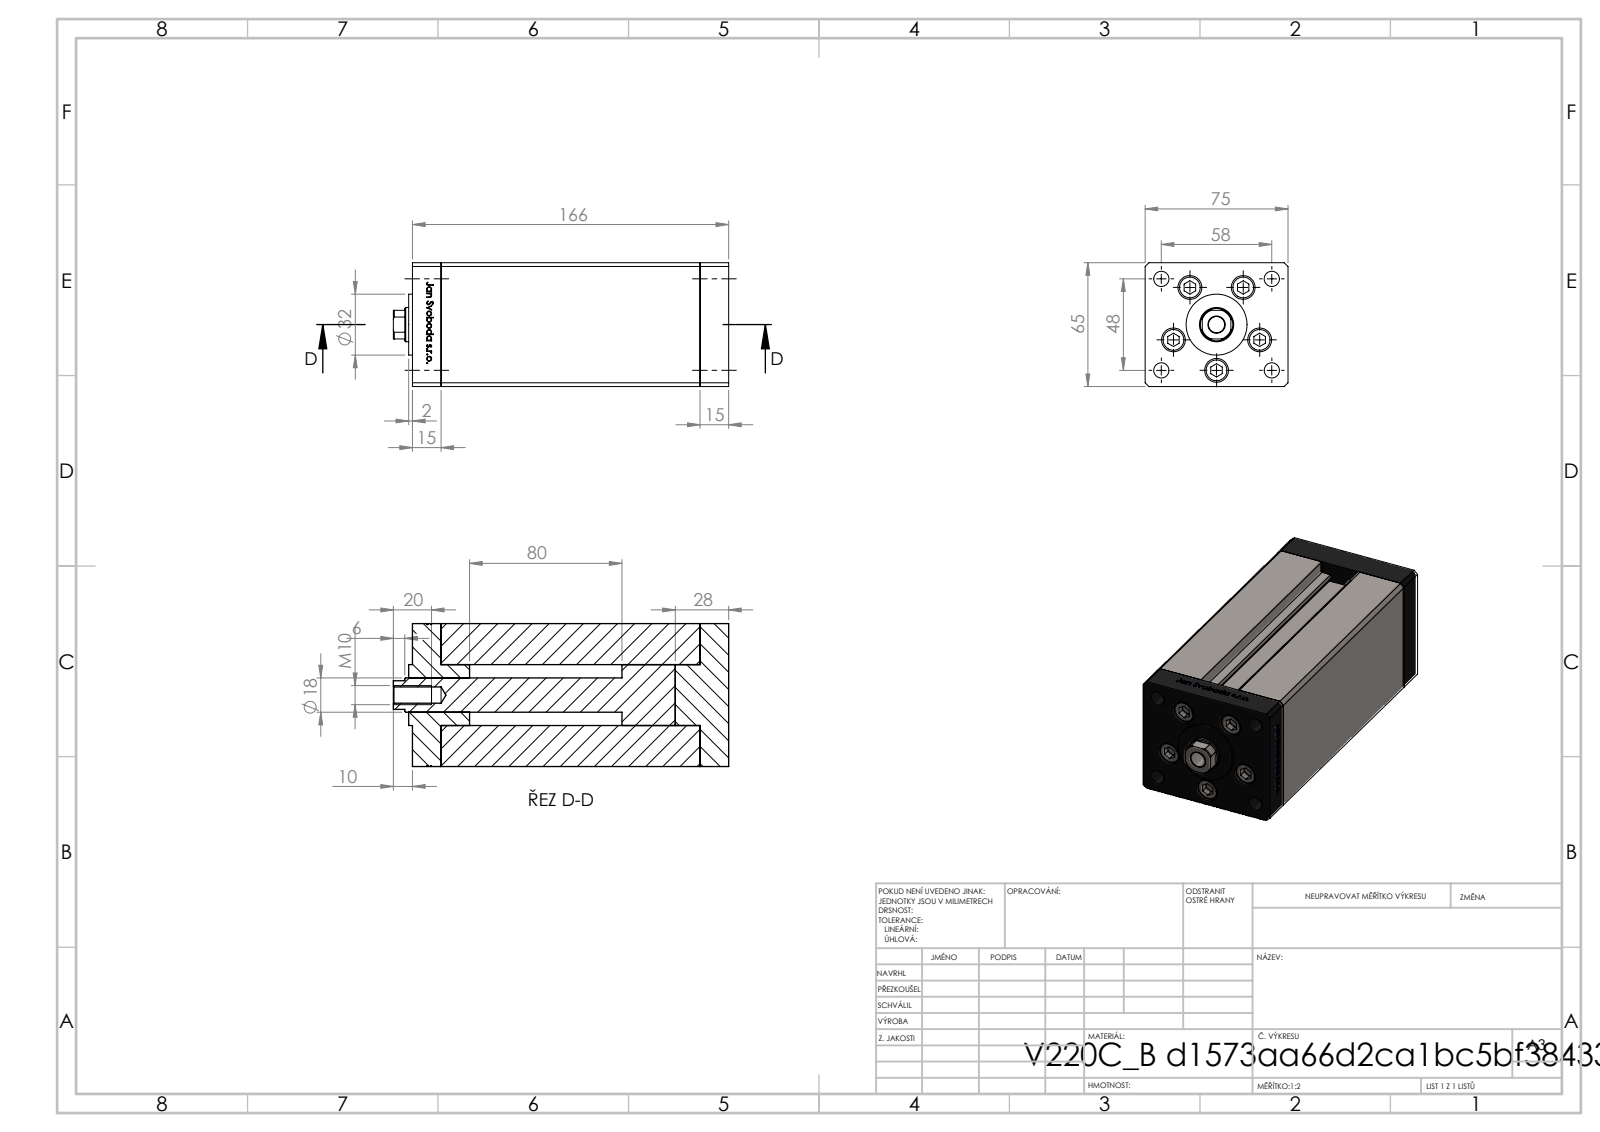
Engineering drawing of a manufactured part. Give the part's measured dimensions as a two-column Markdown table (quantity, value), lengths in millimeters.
| quantity | value |
| --- | --- |
| part name | V220C BACK_B; V220C_B MIDDLE; V220C_VC_B; V220C_FRONT_B (+1 more) |
| STEP written by | SolidWorks 2019 (CONFIG_CONTROL_DESIGN) |
| units | millimeters |
| bodies | 14 solids, 1183 faces (462 planar, 147 cylindrical, 574 other) |
| overall size | 176 × 75 × 65 |
| volume | 722 505 mm³ |
| surface area | 127 353 mm² |
| round holes (diameter × count) | 9 × 5, 12.5 × 5, 8 × 4, 2 × 2, 13.16 × 2, 8.5 × 1, 18 × 1 |
| round bosses / shafts (diameter × count) | 8 × 5, 32 × 1 |
| partial cylindrical surfaces (radius × count) | 0.93 × 2, 8.5 × 1 |
| main face-to-face distances | 75, 65, 15, 136, 151, 166, 28, 13, 54.5, 10.5 |
| hole center spacings | 24, 37.64, 15.67, 17.22, 27.71, 28.83, 29, 32.63 |
